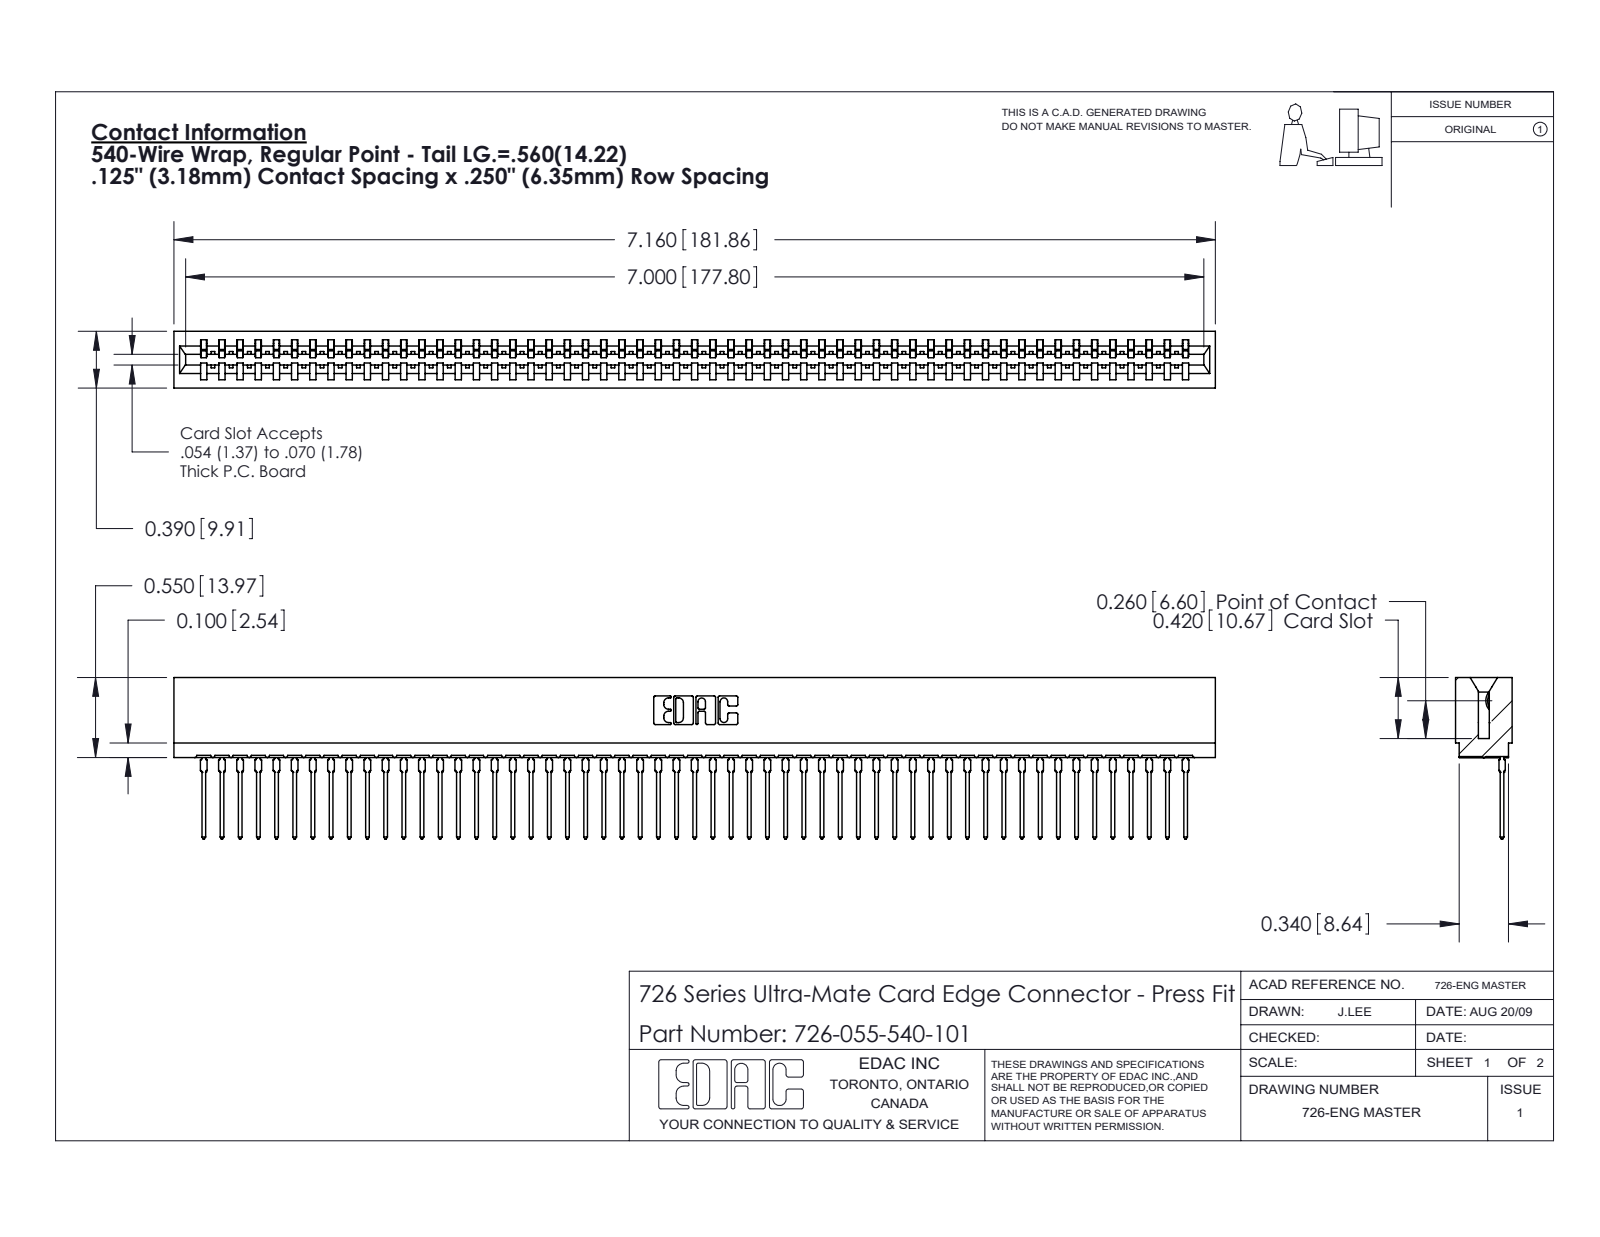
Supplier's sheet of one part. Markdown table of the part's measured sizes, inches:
| quantity | value |
| --- | --- |
| part name | 746-292-001_540; 726 Part_.515 Slot Depth - 01; 726-055-540-101 |
| STEP written by | SolidWorks 2020 (CONFIG_CONTROL_DESIGN) |
| units | inches |
| bodies | 56 solids, 6037 faces (3520 planar, 1087 cylindrical, 1430 other) |
| overall size | 7.16 × 1.109 × 0.39 |
| volume | 0.995 in³ |
| surface area | 39.86 in² |
| partial cylindrical surfaces (radius × count) | 0.021 × 110, 0.015 × 56, 0.01 × 22, 0.007 × 6, 0.031 × 6, 0.005 × 4, 0.011 × 4, 0.026 × 3 |
| main face-to-face distances | 0.057, 0.333, 0.39, 0.025, 0.307, 0.25, 0.083, 0.275, 0.365, 0.032 |
